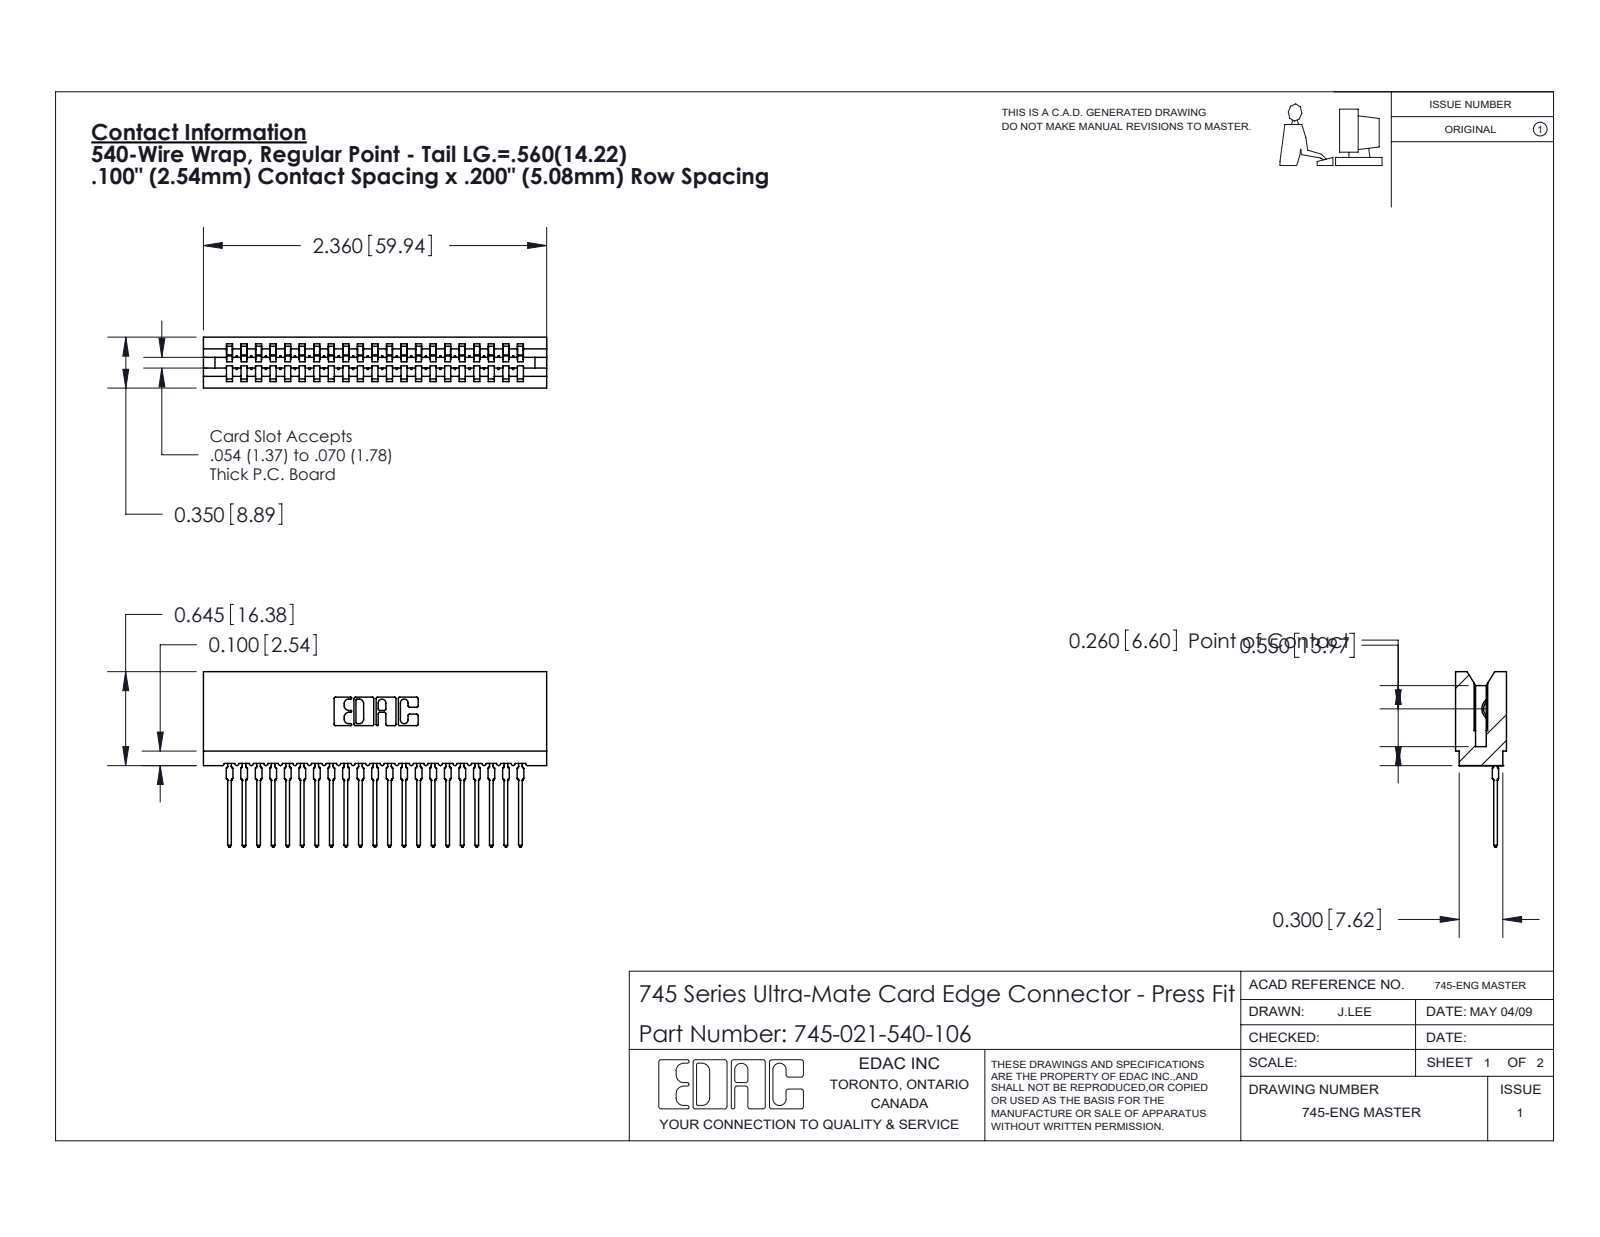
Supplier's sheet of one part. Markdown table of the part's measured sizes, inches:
| quantity | value |
| --- | --- |
| part name | 745-021-540-106; 745-292-001_540; 745 Part_Insulator Option - 06 |
| STEP written by | SolidWorks 2020 (CONFIG_CONTROL_DESIGN) |
| units | inches |
| bodies | 22 solids, 2448 faces (1463 planar, 439 cylindrical, 546 other) |
| overall size | 2.36 × 1.206 × 0.35 |
| volume | 0.327 in³ |
| surface area | 15.23 in² |
| partial cylindrical surfaces (radius × count) | 0.015 × 42, 0.021 × 42, 0.01 × 22, 0.007 × 6, 0.031 × 6, 0.005 × 4, 0.011 × 4, 0.026 × 3 |
| main face-to-face distances | 0.1, 0.2, 0.3, 0.4, 0.35, 0.5, 0.6, 0.7, 0.138, 0.212 |
